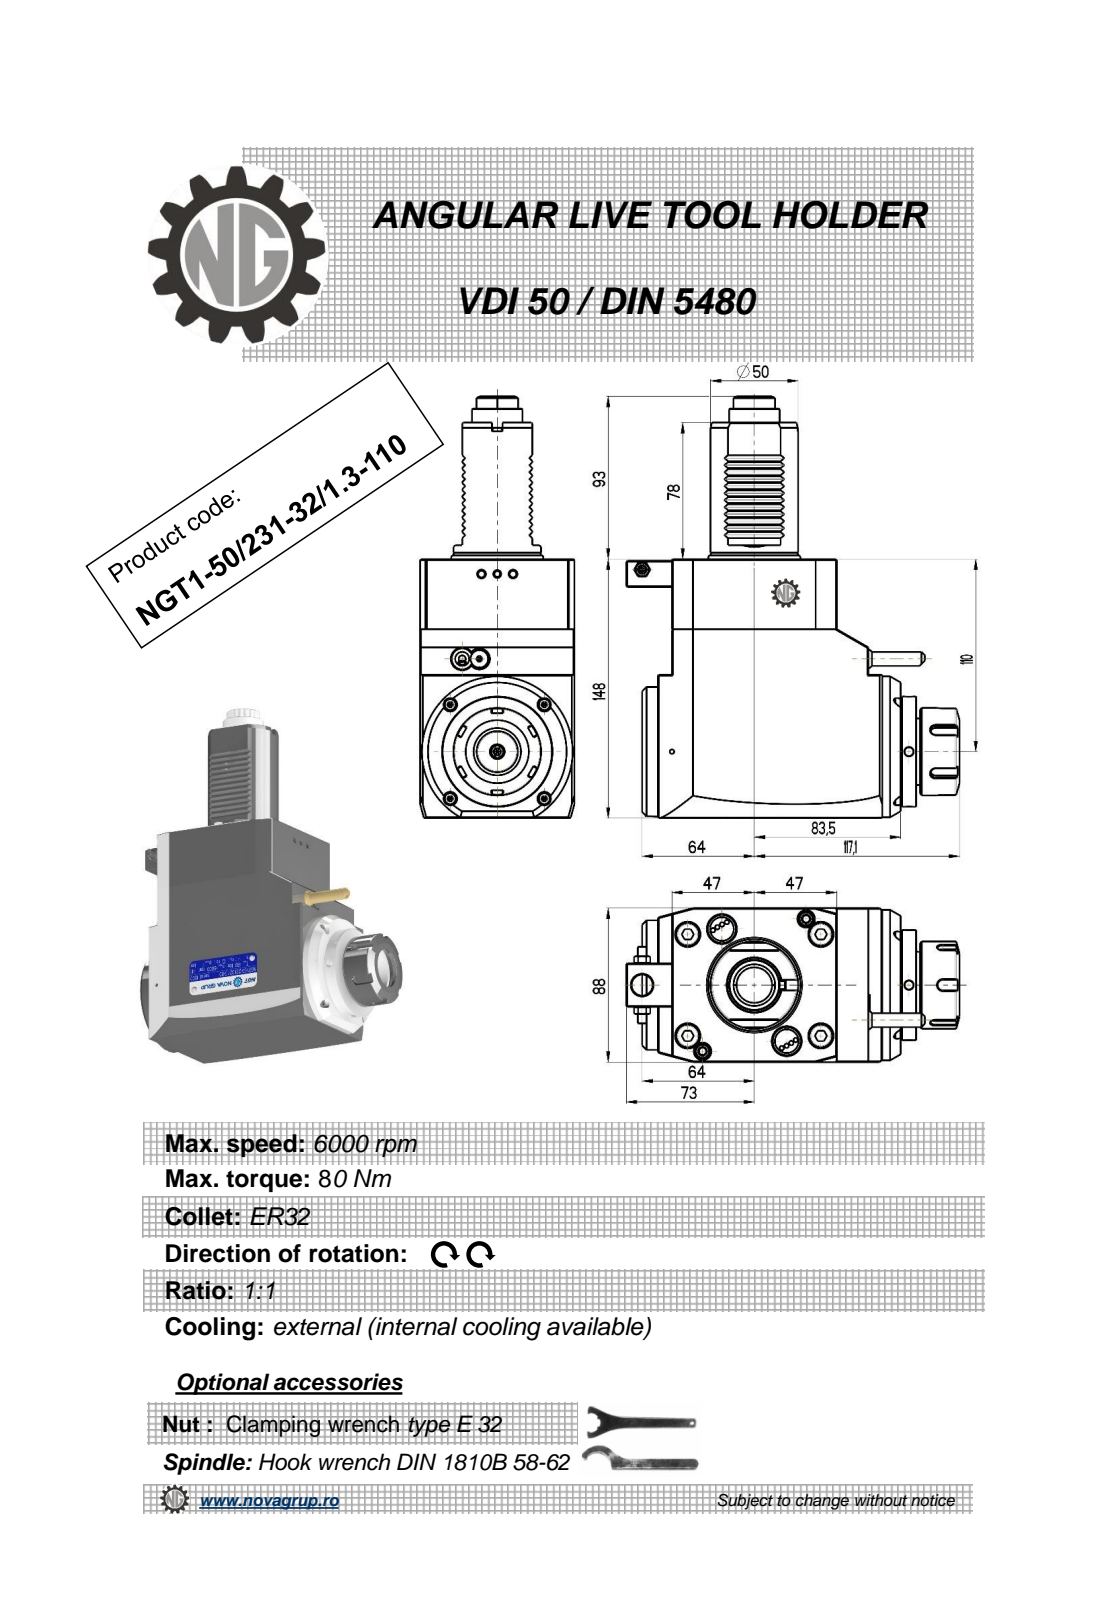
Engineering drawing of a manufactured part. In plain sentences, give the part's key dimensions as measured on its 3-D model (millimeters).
The part is named "NGT1_50_231_32_1_3_110". Its 3-D file was written by "PRO/ENGINEER BY PARAMETRIC TECHNOLOGY CORPORATION, 2010280 (CONFIG_CONTROL_DESIGN)". It is 1 solid with 559 faces: 235 planar, 169 cylindrical and 155 other. Overall it measures 241 by 190.1 by 88 millimeters. Its volume is 1 803 000 cubic millimeters and its surface area 112 274 square millimeters. Round holes: 3 of diameter 5, 1 of diameter 3, 1 of diameter 4.2, 1 of diameter 9.5, 1 of diameter 12, 1 of diameter 27. Round bosses or shafts: 2 of diameter 50, 1 of diameter 86, 1 of diameter 74, 1 of diameter 63, 1 of diameter 50.5, 1 of diameter 41, 1 of diameter 28.8, 1 of diameter 10. Partial cylindrical surfaces (rounded edges, fillets, slot ends): 36 of radius 3.04, 24 of radius 0.3, 12 of radius 0.26, 6 of radius 0.2, 5 of radius 3, 1 of radius 10.56, 1 of radius 11.88, 1 of radius 17.5. The main face-to-face distances are 88, 148, 147.5, 9, 94, 17, 8, 111, 120, 36.5. The hole center spacings are 52.46, 56.65, 101.5, 152.25, 184.38.
